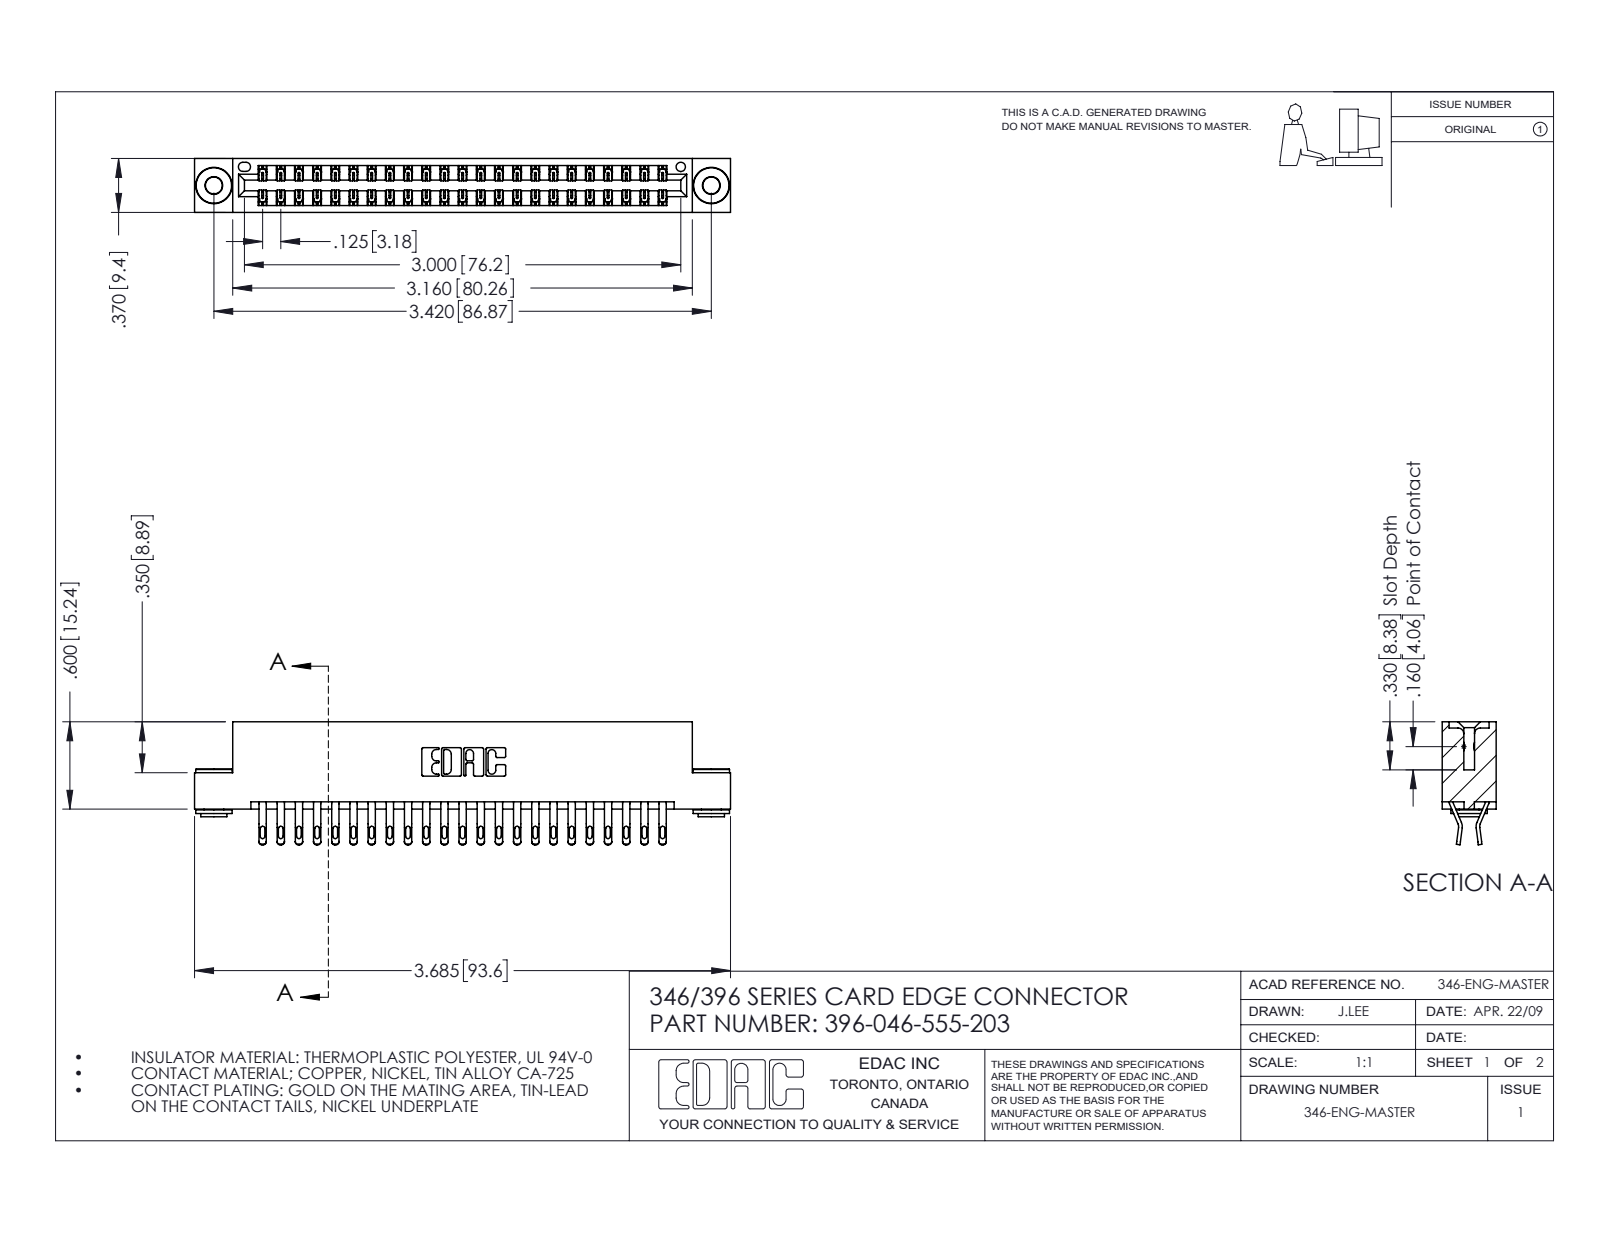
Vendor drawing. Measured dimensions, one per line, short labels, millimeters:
name: 345-250-002_345-250-002-102; 396-046-555-203; 345-292-001_555 Tail; 346 Part_Flush Mounting Lugs - 0.156 Dia-TH
written by: SolidWorks 2016 (CONFIG_CONTROL_DESIGN)
unit: mm
bodies: 49 solids, 2828 faces (1604 planar, 1216 cylindrical, 8 other)
size: 93.6 × 21.5 × 9.4
volume: 9 130 mm³; area: 12 940 mm²
holes: 2× ⌀2.9, 2× ⌀4, 1× ⌀1.6
bosses: 2× ⌀6.4, 2× ⌀4.6, 2× ⌀3.5
rounds: 92× R0.4, 92× R0.5, 69× R0.2, 22× R0.3, 6× R0.2, 6× R0.8, 3× R0.7, 2× R0.3
face distances: 1.2, 8.2, 6.4, 9.4, 0.6, 1.8, 7.6, 7, 3.8, 5.6
hole spacings: 6.2, 81.6, 86.9
